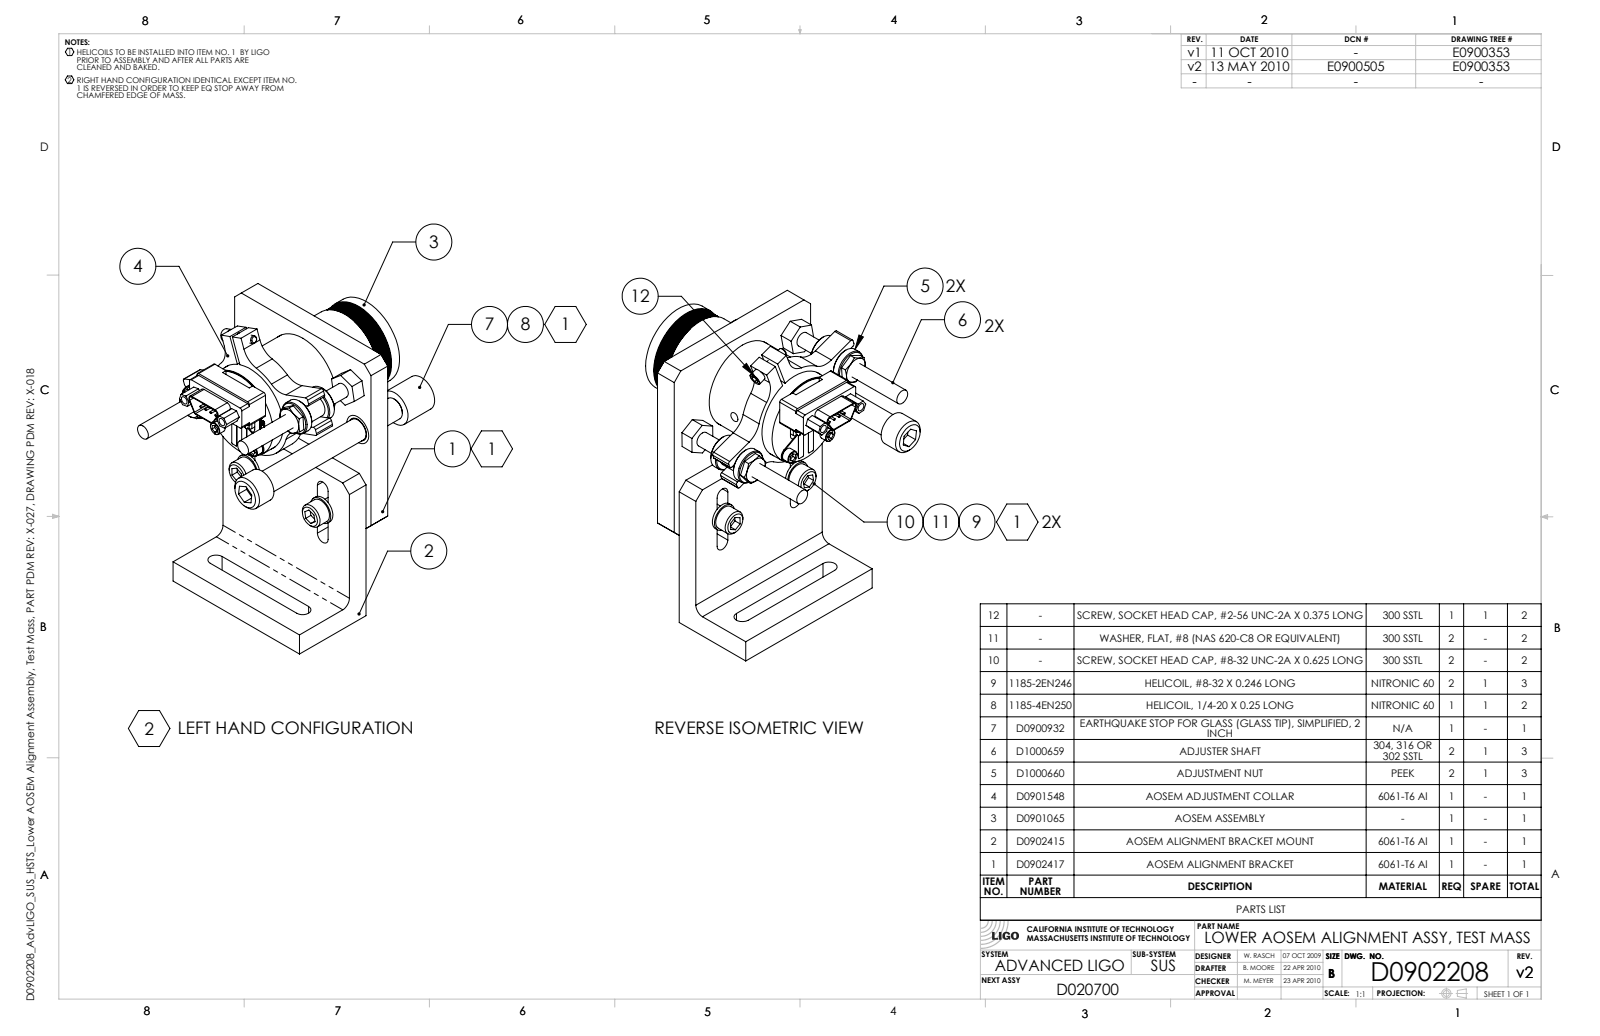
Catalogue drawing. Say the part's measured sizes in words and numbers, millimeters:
The part is named "NAS 620 FLAT WASHERS_________ FLAT WASHERS NAS 620-C8 (OR EQUIV.); D060548_Advanced_LIGO_Fused_Silica_Earthquake_Stop; SST_Socketheadcapscrew_SHCS #8-32 X 0.625; Helicoil_0.25-20 X 0.25 LONG (+8 more)". Its 3-D file was written by "SolidWorks 2009 (CONFIG_CONTROL_DESIGN)". It is 18 solids with 612 faces: 299 planar, 209 cylindrical and 104 other. Overall it measures 95.1 by 91.1 by 74 millimeters. Its volume is 40 660 cubic millimeters and its surface area 35 530 square millimeters. Round holes: 4 of diameter 3.5, 3 of diameter 0.8, 2 of diameter 0.5, 2 of diameter 2, 2 of diameter 2.2, 2 of diameter 2.7, 2 of diameter 4.2, 2 of diameter 4.3, 2 of diameter 4.4, 1 of diameter 1.8, 1 of diameter 2.4, 1 of diameter 5.1. Round bosses or shafts: 9 of diameter 0.5, 5 of diameter 4.2, 3 of diameter 9.5, 3 of diameter 6.4, 3 of diameter 3.6, 2 of diameter 25.3, 2 of diameter 7.7, 2 of diameter 6.8. Partial cylindrical surfaces (rounded edges, fillets, slot ends): 16 of radius 0.6, 6 of radius 6.1, 4 of radius 2, 4 of radius 2, 3 of radius 1.6, 2 of radius 0.5, 2 of radius 0.5, 2 of radius 0.7. The main face-to-face distances are 6.4, 6.4, 6.4, 12.7, 6.3, 48.3, 6.4, 24.3, 23.3, 28.8. The hole center spacings are 20.3, 36.4, 22.1, 36.4, 3.7, 42.5, 10.5, 20.3.
